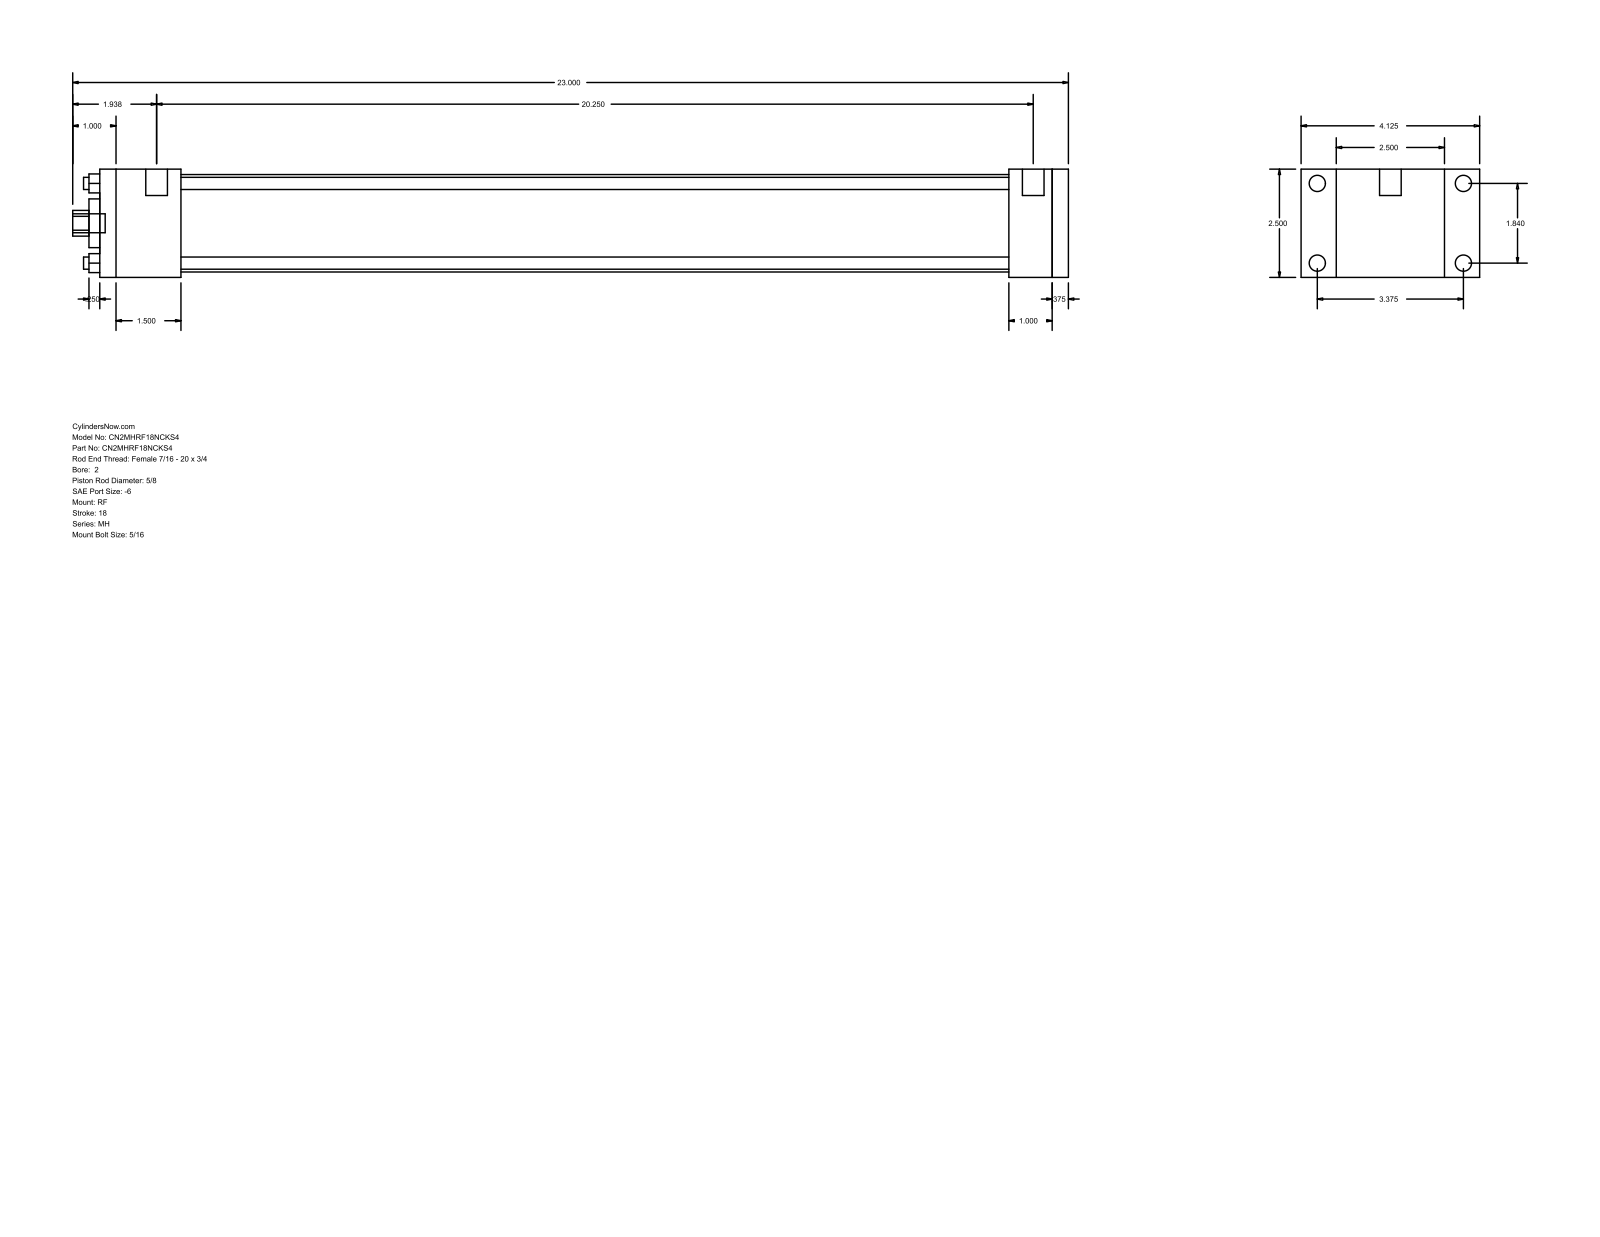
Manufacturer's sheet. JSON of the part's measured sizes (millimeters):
{"part_name": "MH_RF__0200_0.625", "step_written_by": "GSSL Pune (CONFIG_CONTROL_DESIGN)", "units": "millimeters", "bodies": {"solids": 0, "faces": 92, "planar": 64, "cylindrical": 28, "other": 0}, "overall_size": [584.2, 104.78, 63.5], "round_holes": [[7.14, 4], [15.88, 1], [28.57, 1], [57.15, 1]], "round_bosses_or_shafts": [[9.53, 4], [5.56, 4], [12.7, 2], [11.11, 1]], "partial_cylinders_radius": [[7.54, 1]], "face_to_face_distances": [63.5, 568.32, 9.53, 558.79, 25.4, 47.62, 533.39, 485.77, 511.17, 520.7], "hole_center_spacings": [33.05, 46.74, 66.1]}
